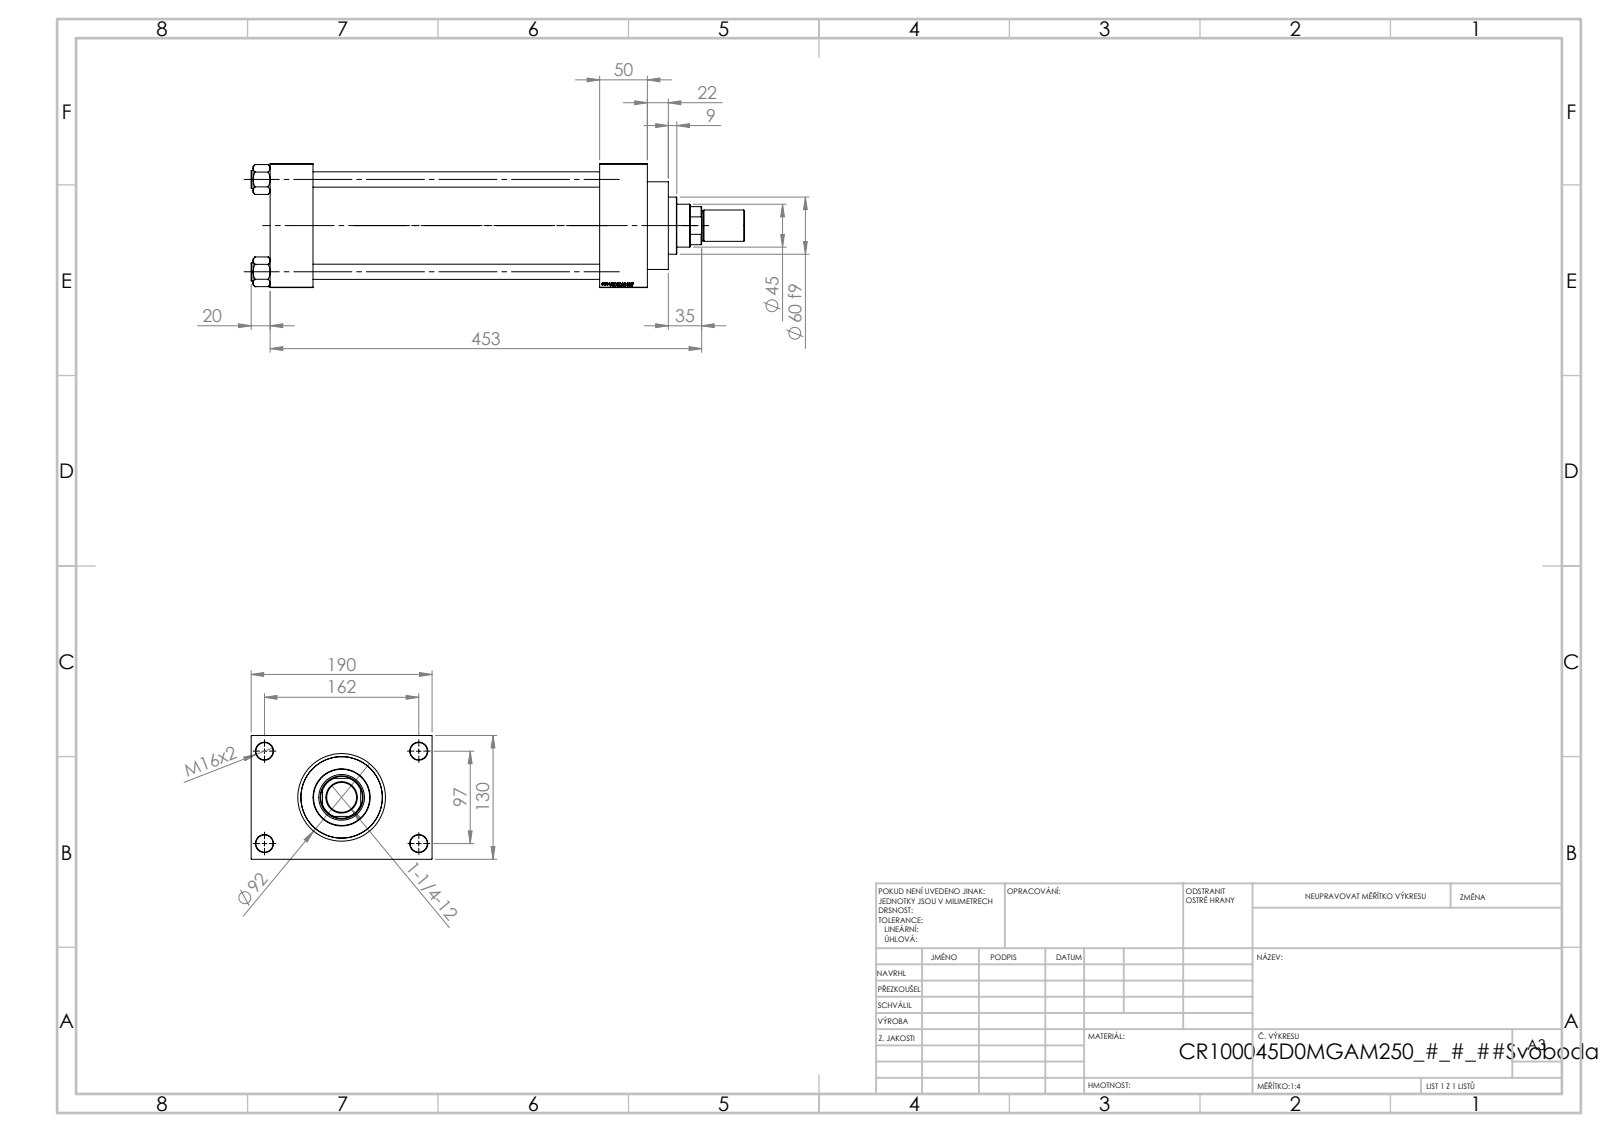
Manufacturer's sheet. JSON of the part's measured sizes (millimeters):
{"part_name": "V215_VC_A; ROD_END_AH; NUT_M5_D; V215CR_VCP_D (+2 more)", "step_written_by": "SolidWorks 2019 (CONFIG_CONTROL_DESIGN)", "units": "millimeters", "bodies": {"solids": 12, "faces": 1166, "planar": 549, "cylindrical": 93, "other": 524}, "overall_size": [518, 190, 130], "volume_mm3": 3419000, "surface_area_mm2": 586466, "round_holes": [[16, 4], [18, 4], [7, 2], [26.44, 2], [35, 2], [31.5, 1], [45, 1], [48, 1], [76, 1], [85.5, 1], [100, 1]], "round_bosses_or_shafts": [[19, 4], [106, 1], [92, 1], [60, 1], [33, 1], [31, 1]], "partial_cylinders_radius": [[22, 1]], "face_to_face_distances": [45, 130, 346, 301, 396, 351, 50, 30, 160, 190], "hole_center_spacings": [32.55, 68.52, 94.41, 96.9, 102.27, 129.45, 161.73, 97]}
